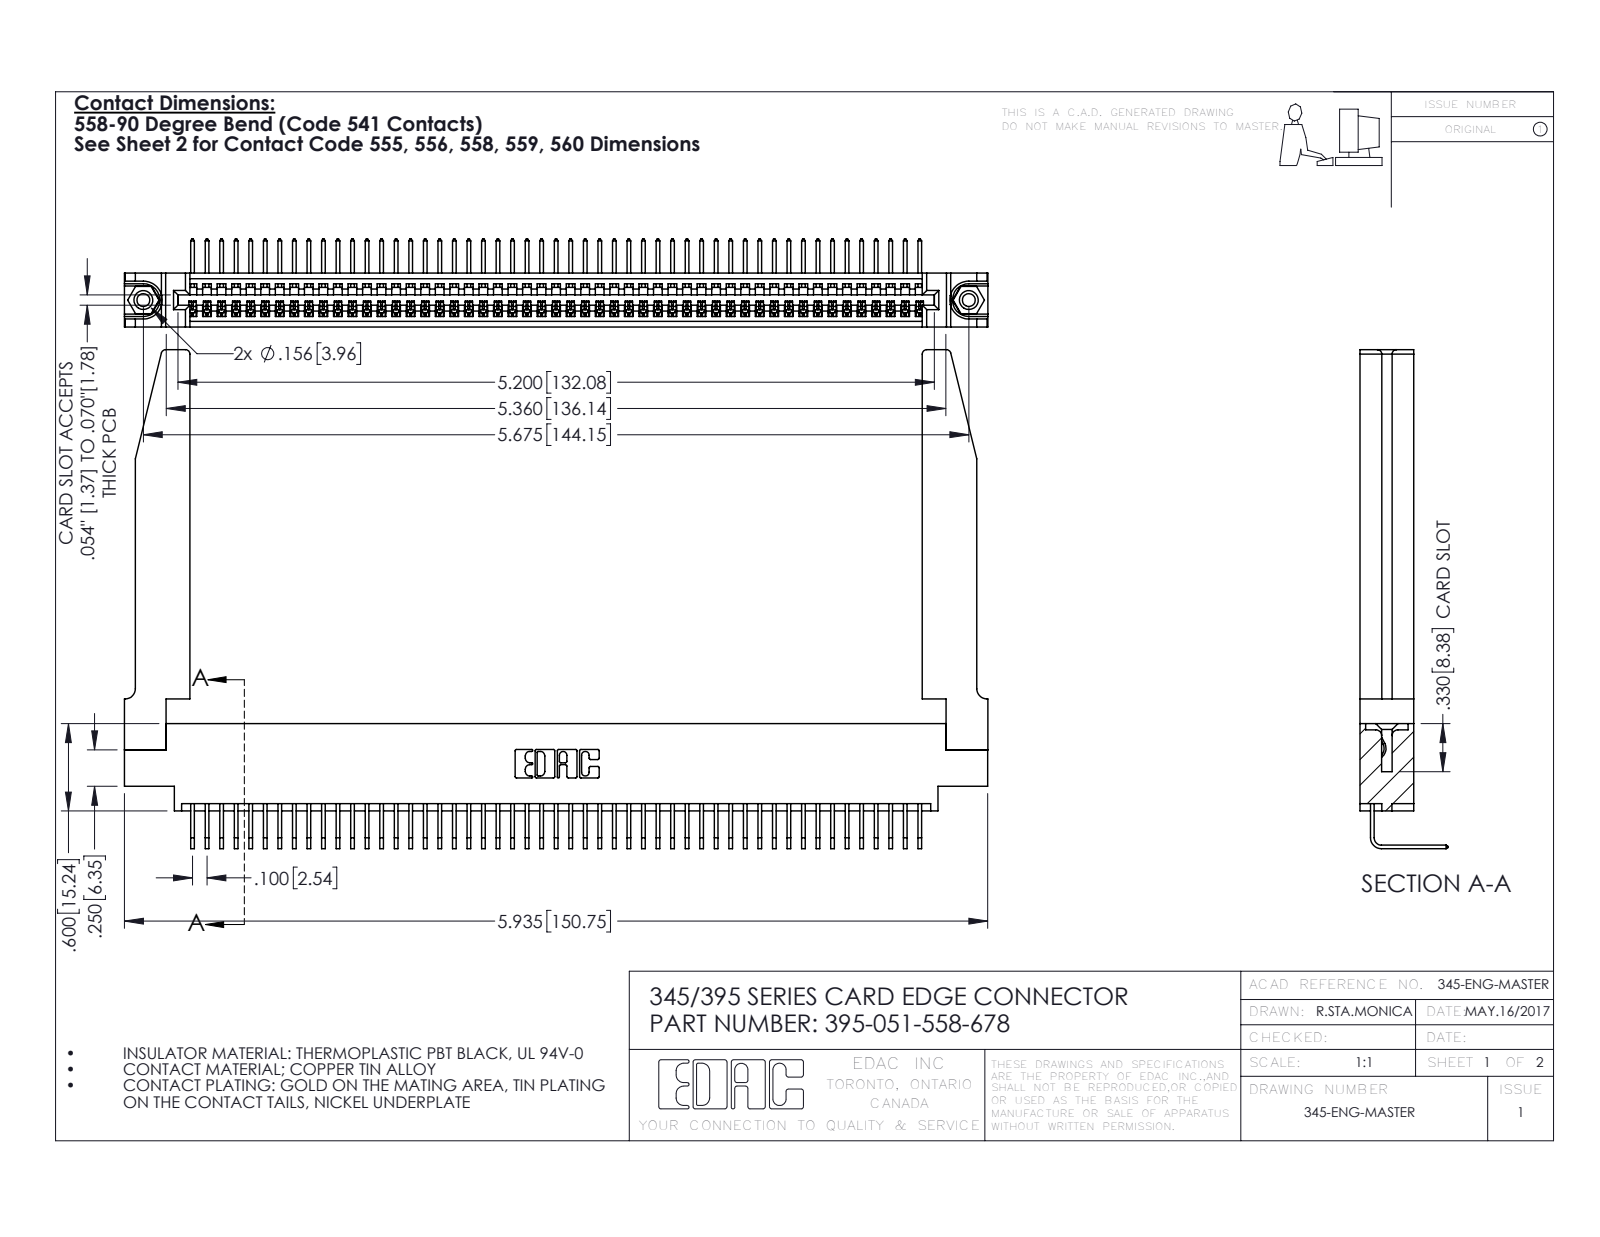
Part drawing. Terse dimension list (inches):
name: 345 Part_0.170 Offset - 0.156 Dia-TH; 345-250-001_345-250-001-102; 395-051-558-678; 345-220-078_345-220-078 (+1 more)
written by: SolidWorks 2016 (CONFIG_CONTROL_DESIGN)
unit: in
bodies: 56 solids, 3424 faces (2368 planar, 1004 cylindrical, 52 other)
size: 5.936 × 3.429 × 0.605
volume: 1.356 in³; area: 42.31 in²
holes: 2× ⌀0.089, 2× ⌀0.125, 2× ⌀0.156, 1× ⌀0.064
bosses: 2× ⌀0.155
rounds: 102× R0.006, 22× R0.01, 8× R0.03, 6× R0.007, 6× R0.031, 3× R0.026, 2× R0.031, 2× R0.04
face distances: 0.37, 0.072, 0.298, 0.098, 0.272, 0.025, 0.2, 0.225, 0.148, 0.15
hole spacings: 0.27, 5.439, 5.675
